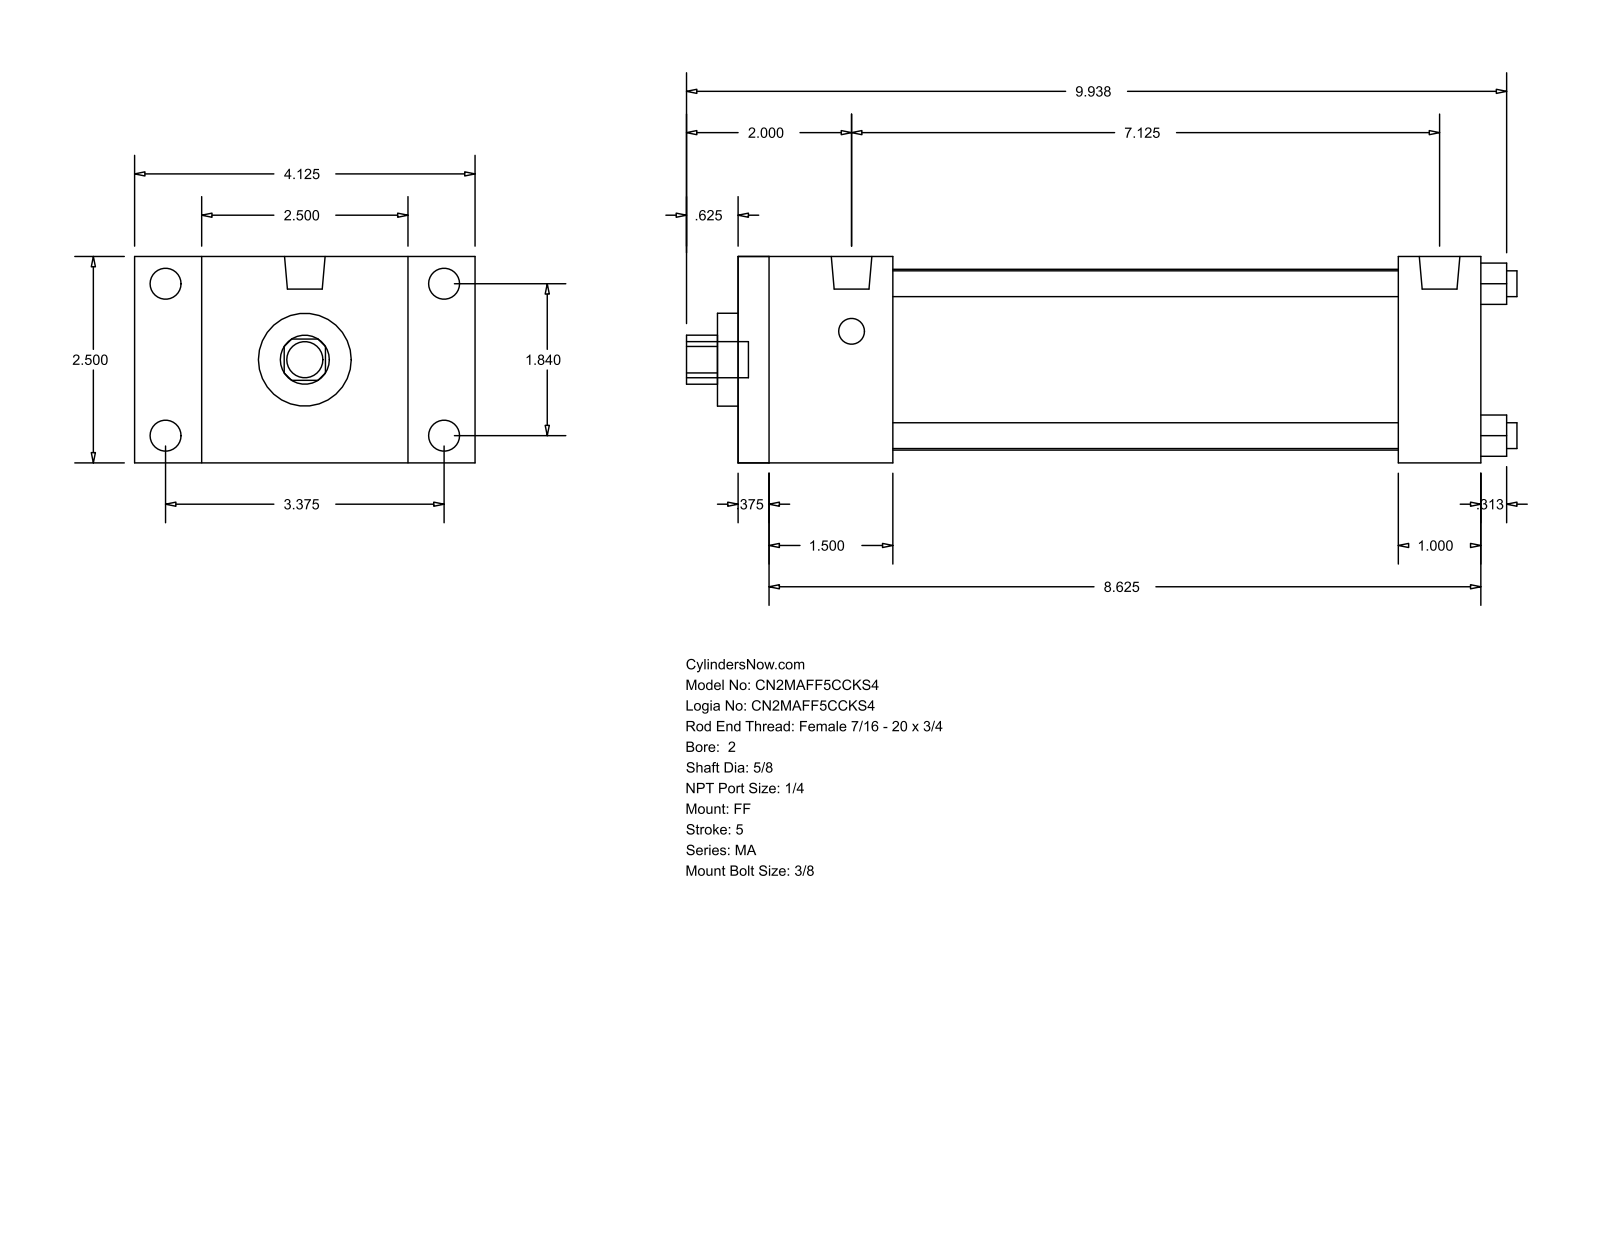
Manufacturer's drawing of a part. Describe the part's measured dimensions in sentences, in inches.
The part is named "MA_FF__0200_0.625". Its 3-D file was written by "GSSL Pune (CONFIG_CONTROL_DESIGN)". It is 0 solids with 92 faces: 64 planar, 28 cylindrical and 0 other. Overall it measures 10.063 by 4.125 by 2.5 inches. Round holes: 4 of diameter 0.313, 1 of diameter 0.625, 1 of diameter 1.125, 1 of diameter 2.19. Round bosses or shafts: 4 of diameter 0.375, 4 of diameter 0.313, 2 of diameter 0.492, 1 of diameter 0.437. Partial cylindrical surfaces (rounded edges, fillets, slot ends): 1 of radius 0.297. The main face-to-face distances are 2.5, 9, 0.375, 8.625, 1, 1.5, 1.875, 8, 7.625, 6.125. The hole center spacings are 1.301, 1.84, 2.602.
